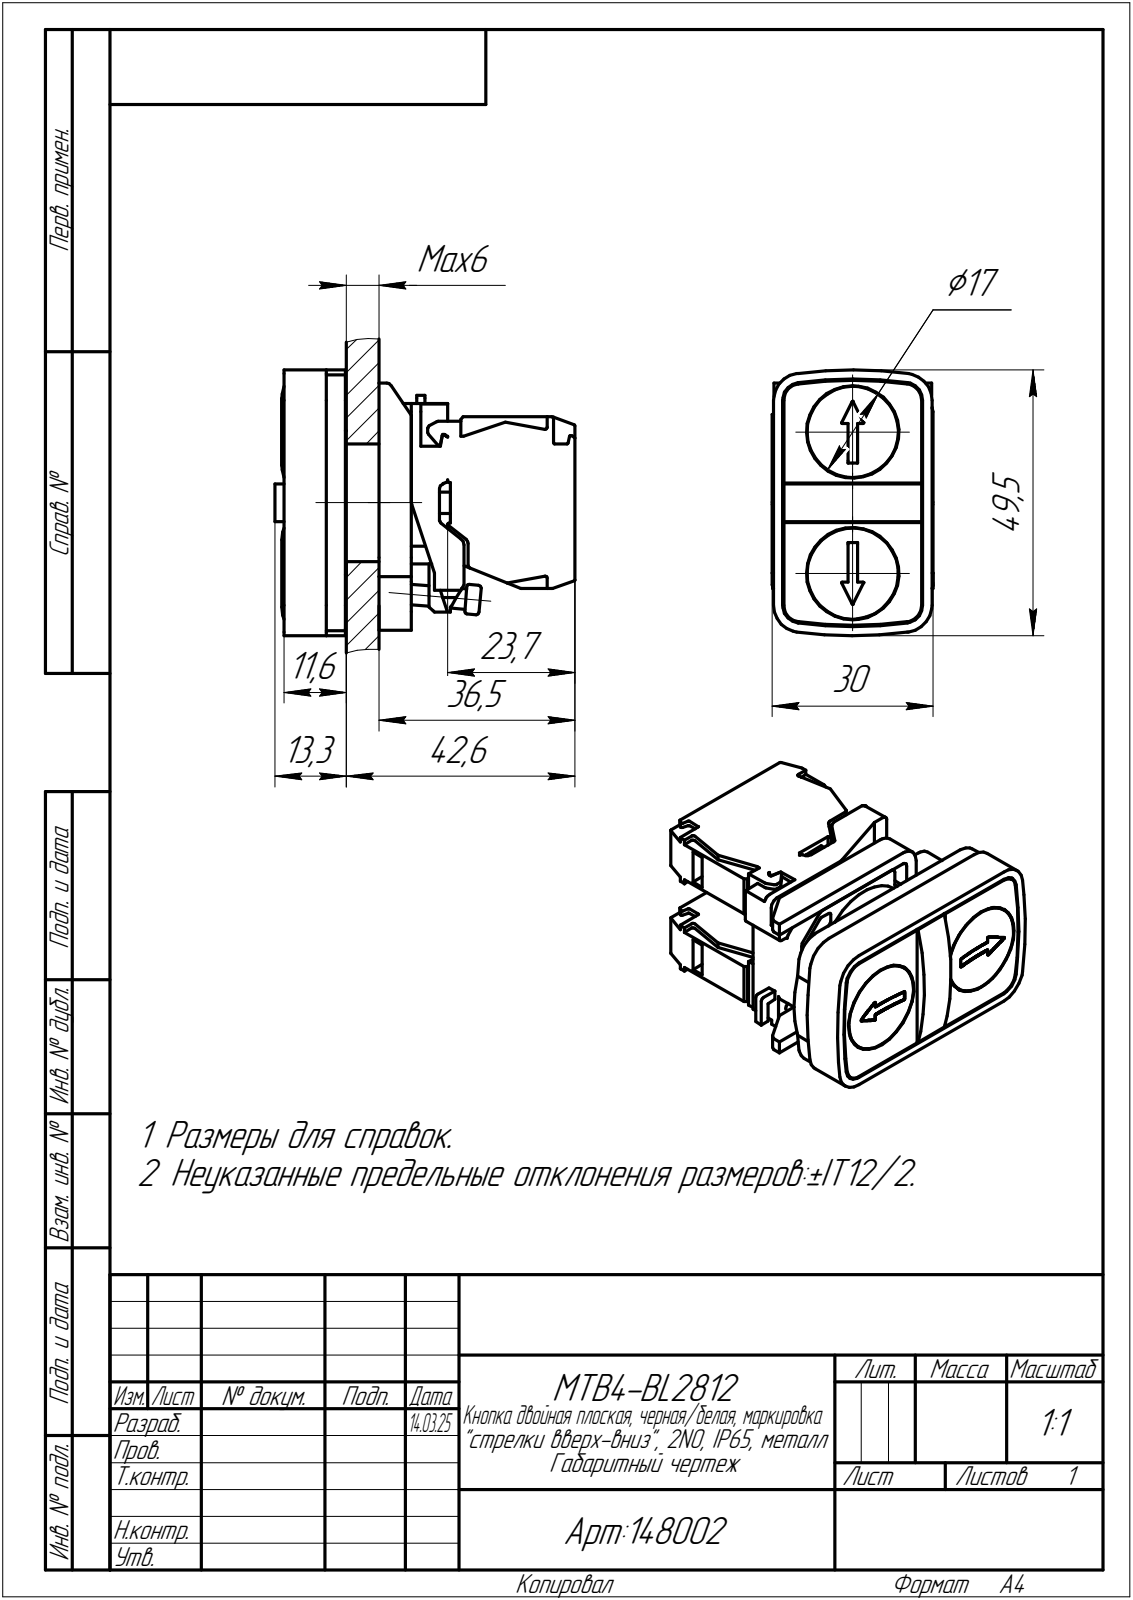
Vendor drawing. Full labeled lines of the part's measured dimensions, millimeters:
Part name (STEP PRODUCT): MTB4-BL2812
STEP written by: C3D Toolkit (CONFIG_CONTROL_DESIGN)
Units: millimetres
Bodies: 2 solids, 537 faces (340 planar, 167 cylindrical, 30 other)
Overall size (bounding box): 55.9 × 49.5 × 30
Volume: 41 978 mm³ · Surface area: 17 972 mm²
Round holes (diameter × count): ⌀1.5 ×2, ⌀17.2 ×2, ⌀20.5 ×1
Round bosses / shafts (diameter × count): ⌀17 ×2, ⌀26.8 ×1, ⌀22 ×1, ⌀5.5 ×1, ⌀3.8 ×1
Partial cylindrical surfaces — rounded edges, fillets, slot ends (radius × count): R0.5 ×23, R0.1 ×10, R0.2 ×10, R0.8 ×7, R1 ×5, R1.02 ×4, R3.1 ×4, R3.3 ×4
Main face-to-face distances: 20, 9.9, 11.4, 2.5, 29.9, 10.1, 1.95, 1.82, 29.75, 17.7
Hole centre spacings: 13.2, 11.56, 11.88, 17.84, 19.73, 23.22, 26.4, 29.18
